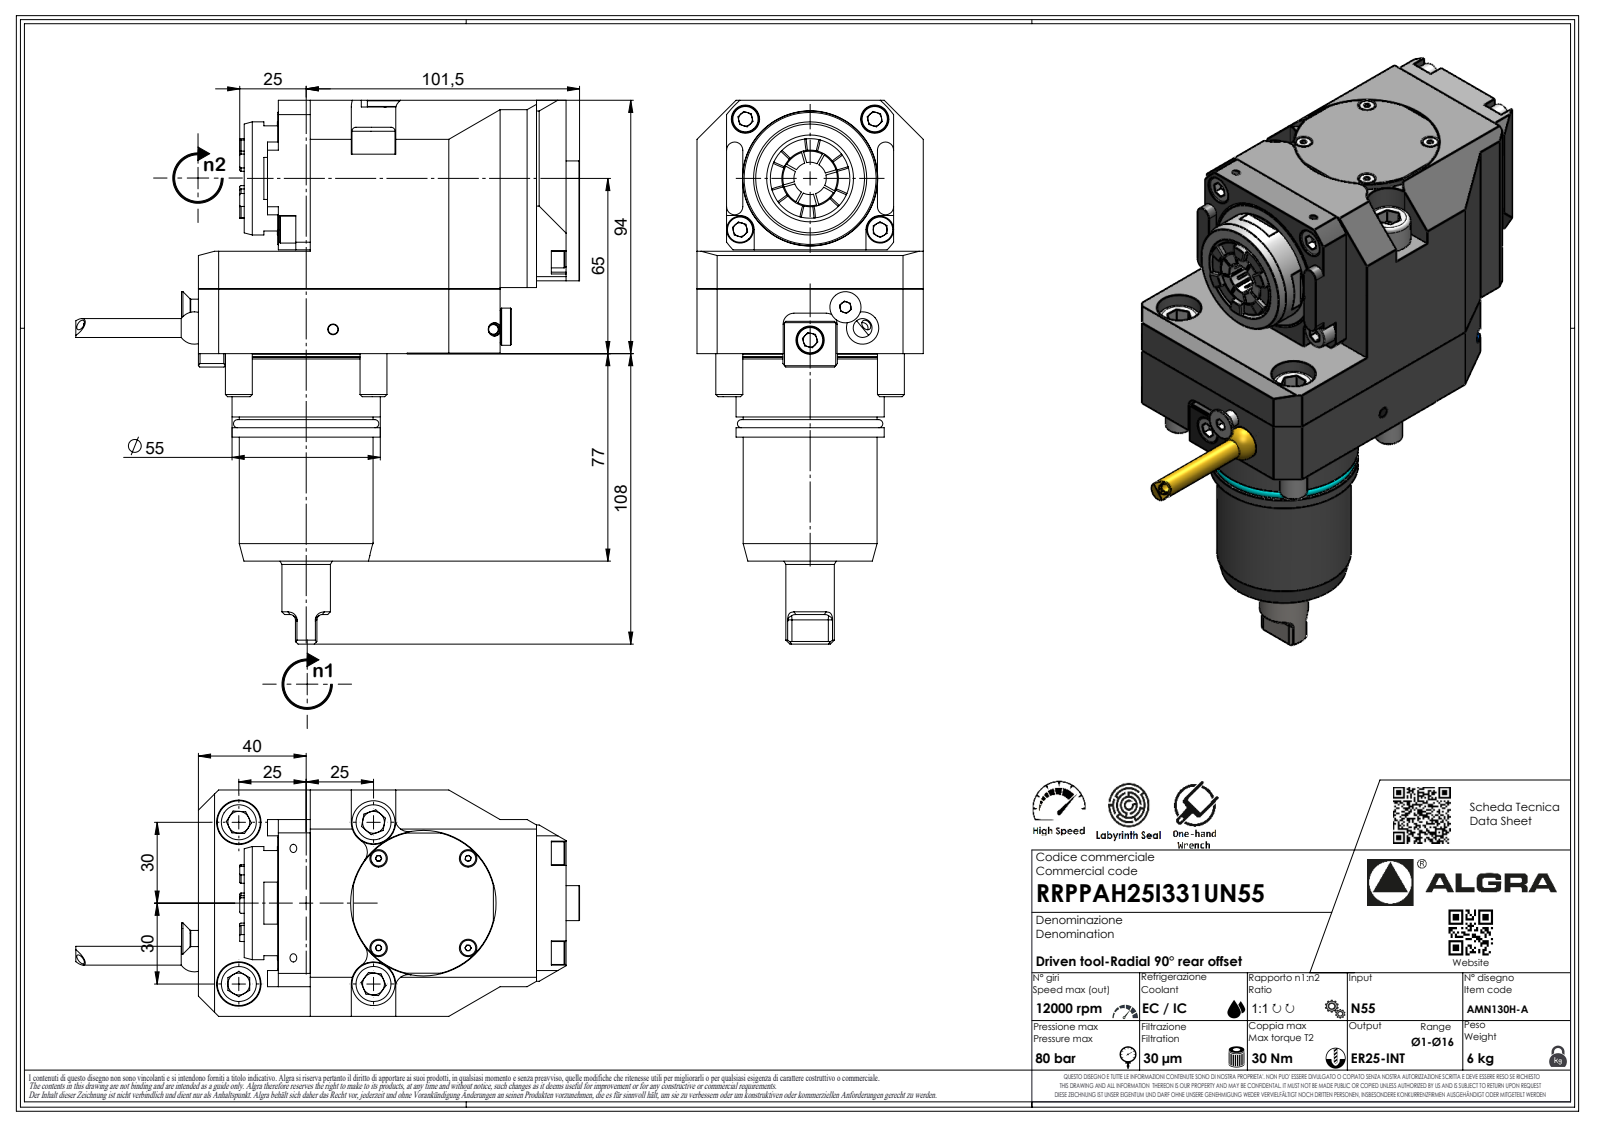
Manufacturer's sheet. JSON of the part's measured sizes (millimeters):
{"part_name": "RRPPAH25I331UN55", "step_written_by": "SolidWorks 2023 (AUTOMOTIVE_DESIGN)", "units": "millimeters", "bodies": {"solids": 1, "faces": 532, "planar": 332, "cylindrical": 78, "other": 122}, "overall_size": [201.8, 187, 84], "volume_mm3": 978588, "surface_area_mm2": 78264, "round_holes": [[2.1, 1], [4, 1], [54, 1]], "round_bosses_or_shafts": [[10, 4], [16, 2], [55, 1], [54.6, 1], [49.7, 1], [42, 1], [18, 1], [7, 1]], "partial_cylinders_radius": [[0.33, 7], [0.52, 7], [2, 7], [3.7, 7], [3, 4], [5, 4], [8.25, 3], [0.21, 1]], "face_to_face_distances": [84, 24.5, 11, 94, 56, 38, 37.8, 93.8, 73, 95]}
